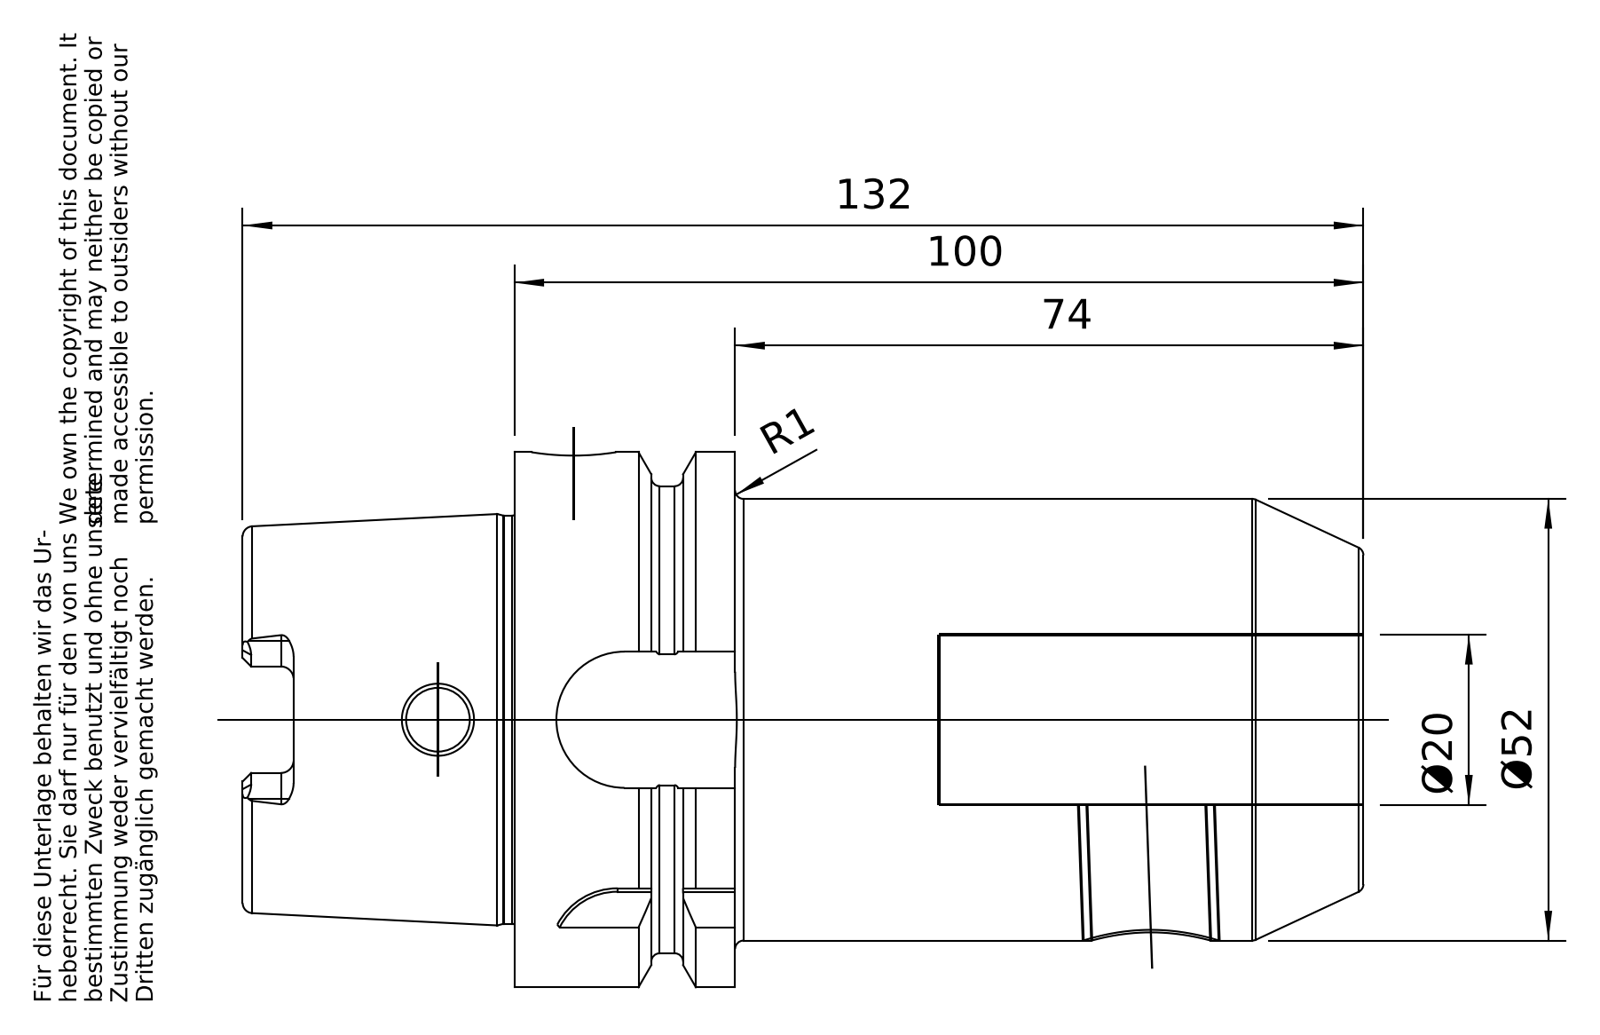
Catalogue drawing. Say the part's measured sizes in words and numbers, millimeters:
The part is named "A63-030-20". Its 3-D file was written by "PRO/ENGINEER BY PARAMETRIC TECHNOLOGY CORPORATION, 2010430 (CONFIG_CONTROL_DESIGN)". It is 1 solid with 180 faces: 58 planar, 52 cylindrical and 70 other. Overall it measures 132 by 63 by 63 millimeters. Its volume is 214 835 cubic millimeters and its surface area 38 089 square millimeters. Round holes: 1 of diameter 7.5, 1 of diameter 10, 1 of diameter 14, 1 of diameter 16, 1 of diameter 16.92, 1 of diameter 18.32, 1 of diameter 18.66, 1 of diameter 20, 1 of diameter 34, 1 of diameter 40. Round bosses or shafts: 1 of diameter 63, 1 of diameter 55, 1 of diameter 52, 1 of diameter 48.04, 1 of diameter 18. Partial cylindrical surfaces (rounded edges, fillets, slot ends): 6 of radius 1.5, 4 of radius 3, 1 of radius 8, 1 of radius 8.02, 1 of radius 9.02. The main face-to-face distances are 100, 26, 74, 50, 10, 16, 90, 32, 42, 58.
